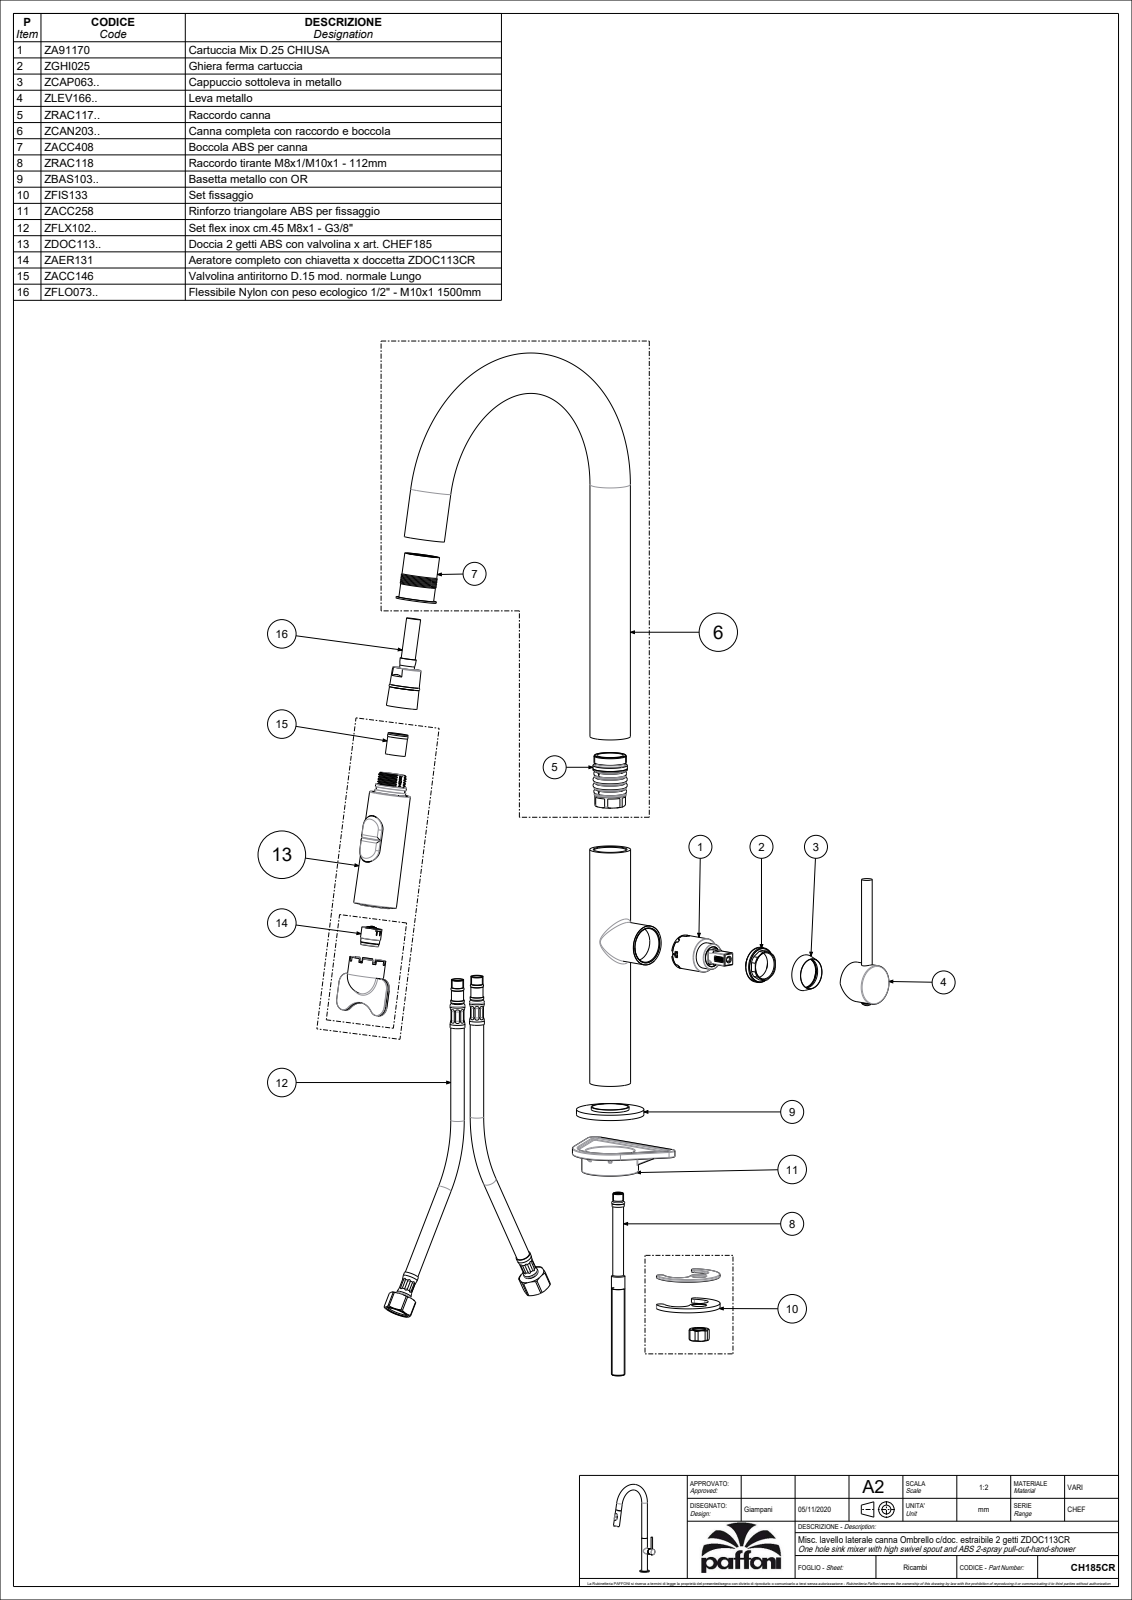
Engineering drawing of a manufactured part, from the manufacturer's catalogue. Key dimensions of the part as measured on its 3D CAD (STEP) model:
Part name (STEP PRODUCT): CH185CR
STEP written by: CREO PARAMETRIC BY PTC INC, 2020044 (CONFIG_CONTROL_DESIGN)
Units: millimetres
Bodies: 4 solids, 611 faces (253 planar, 175 cylindrical, 183 other)
Overall size (bounding box): 480.2 × 251.57 × 88.53
Volume: 255 376 mm³ · Surface area: 151 244 mm²
Round holes (diameter × count): ⌀3 ×2, ⌀23 ×2, ⌀27 ×2, ⌀0.56 ×1, ⌀4.2 ×1, ⌀8.1 ×1, ⌀25.7 ×1, ⌀26 ×1, ⌀28.4 ×1, ⌀28.5 ×1, ⌀29.8 ×1
Round bosses / shafts (diameter × count): ⌀30 ×2, ⌀50 ×1, ⌀30.3 ×1, ⌀29.2 ×1, ⌀29 ×1, ⌀26.8 ×1, ⌀26 ×1, ⌀7.9 ×1
Partial cylindrical surfaces — rounded edges, fillets, slot ends (radius × count): R0.5 ×14, R1 ×9, R0.3 ×8, R0.2 ×4, R2 ×3, R9.4 ×3, R0.1 ×2, R2.5 ×2
Main face-to-face distances: 4, 180, 176, 82.15, 82.11, 1.45, 10.55, 15.4, 1.5, 9
Hole centre spacings: 54.4, 317.72
